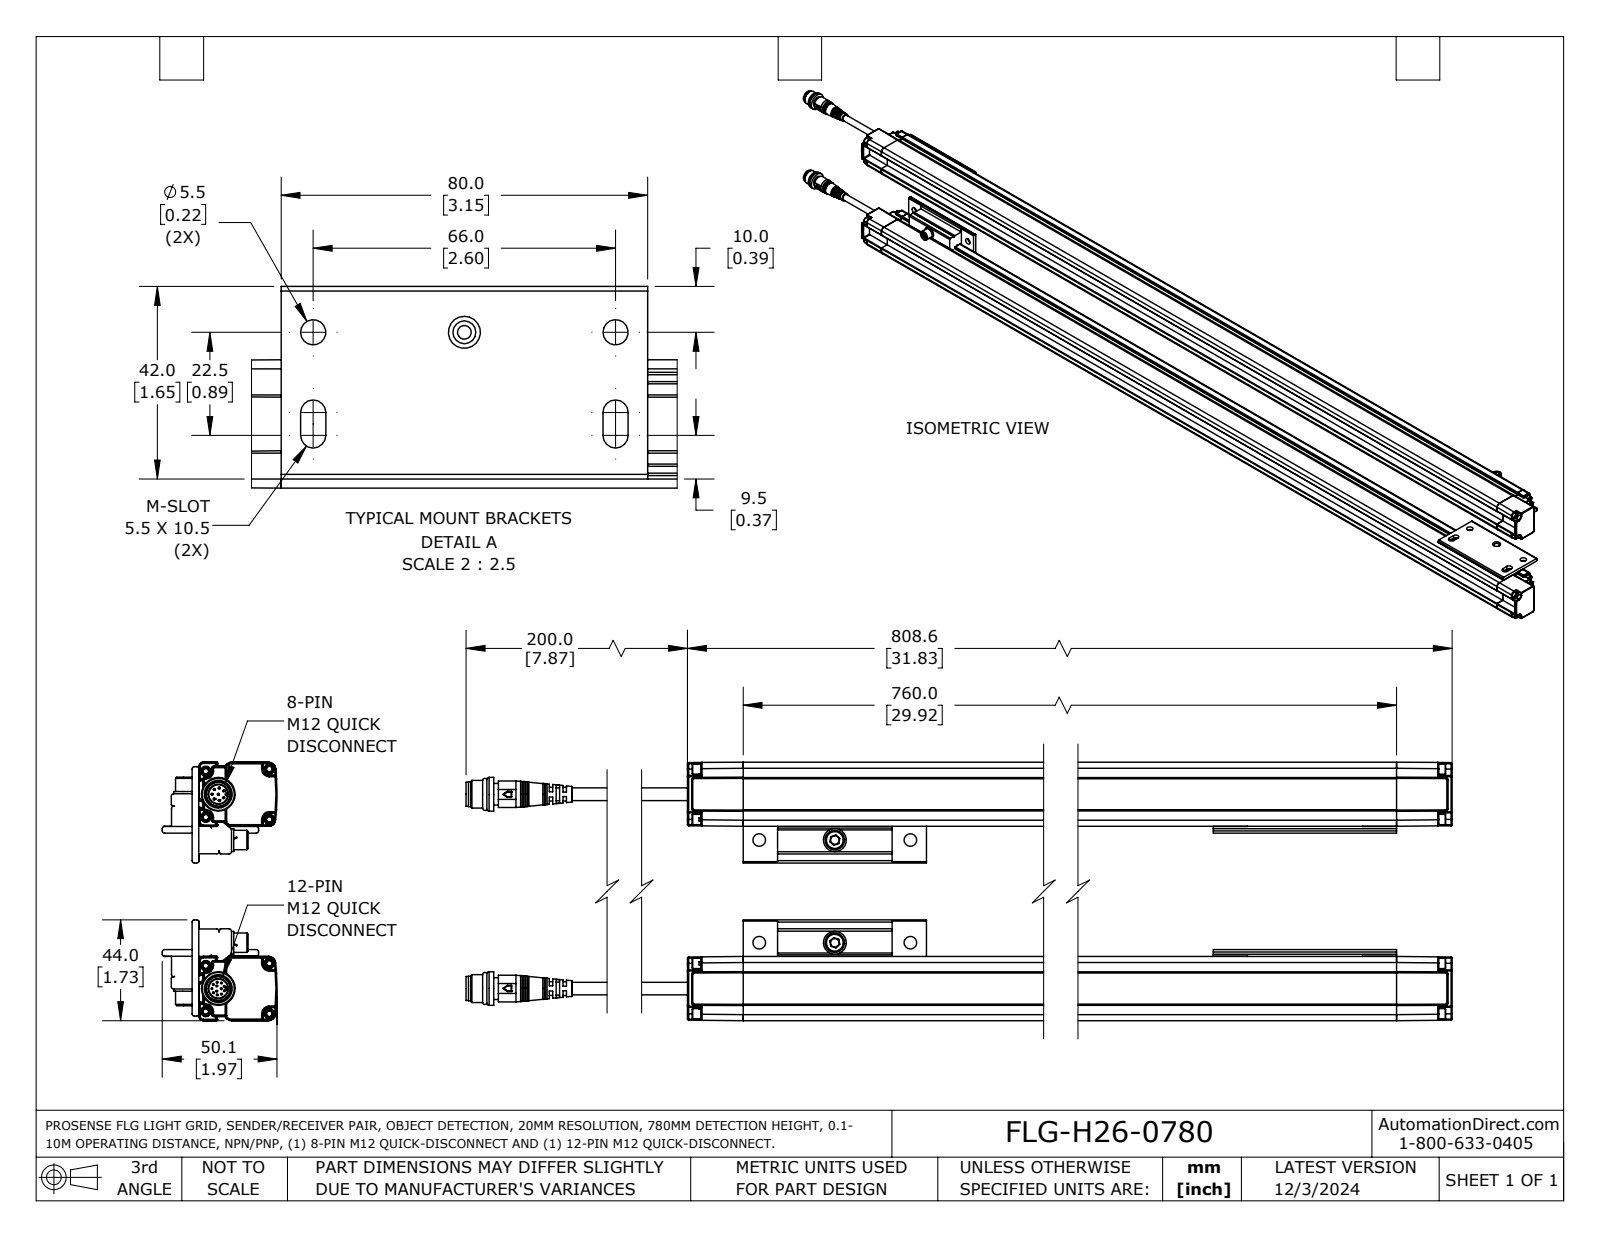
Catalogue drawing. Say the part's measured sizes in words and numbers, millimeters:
The part is named "FLG-H26-0780". Its 3-D file was written by "SolidWorks 2023 (AUTOMOTIVE_DESIGN)". It is 10 solids with 1668 faces: 816 planar, 456 cylindrical and 396 other. Overall it measures 900.55 by 112.8 by 50.09 millimeters. Its volume is 1 327 000 cubic millimeters and its surface area 341 093 square millimeters. Round holes: 16 of diameter 0.4, 6 of diameter 5.5, 4 of diameter 2.5, 3 of diameter 5, 2 of diameter 8.3. Round bosses or shafts: 20 of diameter 0.8, 8 of diameter 4.5, 8 of diameter 3, 4 of diameter 5.5, 4 of diameter 1.5, 3 of diameter 10, 3 of diameter 8.5, 3 of diameter 3.7. Partial cylindrical surfaces (rounded edges, fillets, slot ends): 142 of radius 0.5, 40 of radius 1, 20 of radius 0.25, 12 of radius 0.2, 12 of radius 0.3, 12 of radius 2.75, 6 of radius 2.55, 4 of radius 1.25. The main face-to-face distances are 84.8, 28, 1.8, 7.25, 20.75, 24.65, 56.8, 112.8, 26.45, 3. The hole center spacings are 2.75, 33, 4.15, 24.87, 55.64, 5.45, 44.8, 66.
